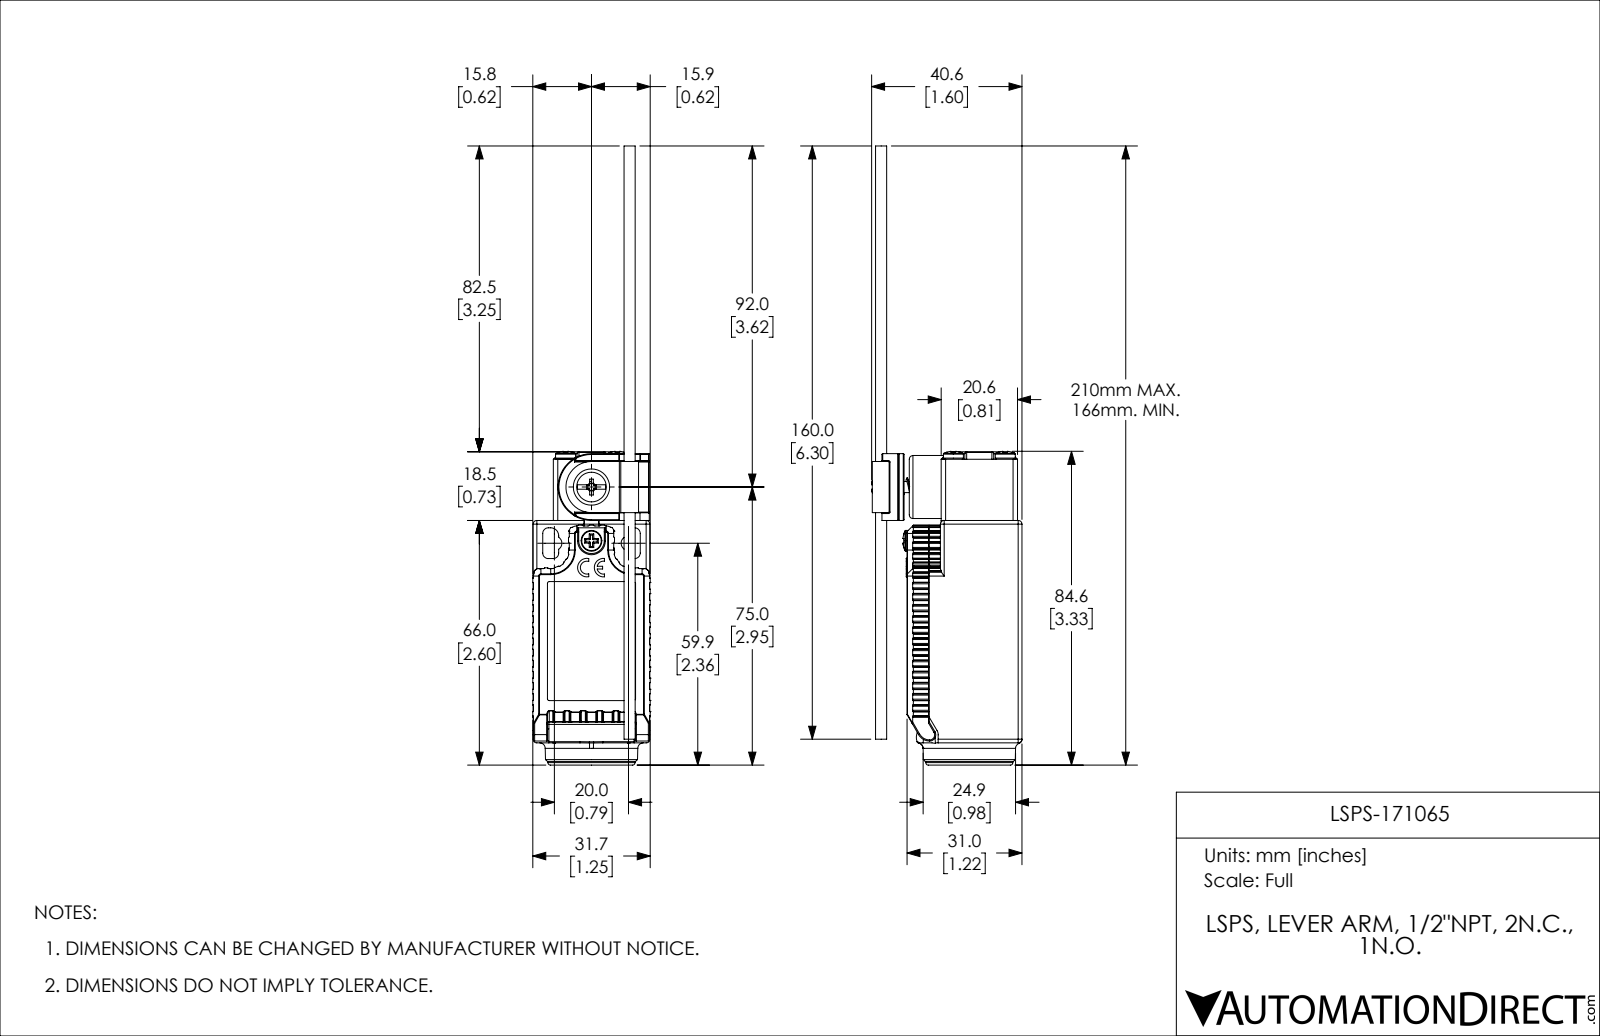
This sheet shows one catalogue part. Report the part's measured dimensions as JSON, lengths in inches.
{"part_name": "171-LSPS-Lever Arm (STEP format)", "step_written_by": "SolidWorks 2015 (CONFIG_CONTROL_DESIGN)", "units": "inches", "bodies": {"solids": 13, "faces": 2495, "planar": 1086, "cylindrical": 1054, "other": 355}, "overall_size": [6.575, 1.598, 1.248], "volume_in3": 1.927, "surface_area_in2": 51.15, "round_holes": [[0.091, 5], [0.11, 4], [0.126, 4], [0.217, 4], [0.157, 2], [0.197, 1], [0.205, 1], [0.283, 1], [0.315, 1], [0.386, 1], [0.496, 1], [0.614, 1]], "round_bosses_or_shafts": [[0.067, 5], [0.213, 4], [0.098, 4], [0.925, 1], [0.697, 1], [0.669, 1], [0.394, 1], [0.26, 1]], "partial_cylinders_radius": [[0.02, 129], [0.008, 125], [0.004, 92], [0.012, 37], [0.013, 32], [0.039, 23], [0.079, 18], [0.031, 16]], "face_to_face_distances": [1.152, 0.089, 1.24, 0.039, 0.126, 0.063, 1.063, 1.173, 0.937, 1.11], "hole_center_spacings": [0.39, 0.551, 0.306, 0.324, 0.471, 0.646, 0.78, 0.787]}
